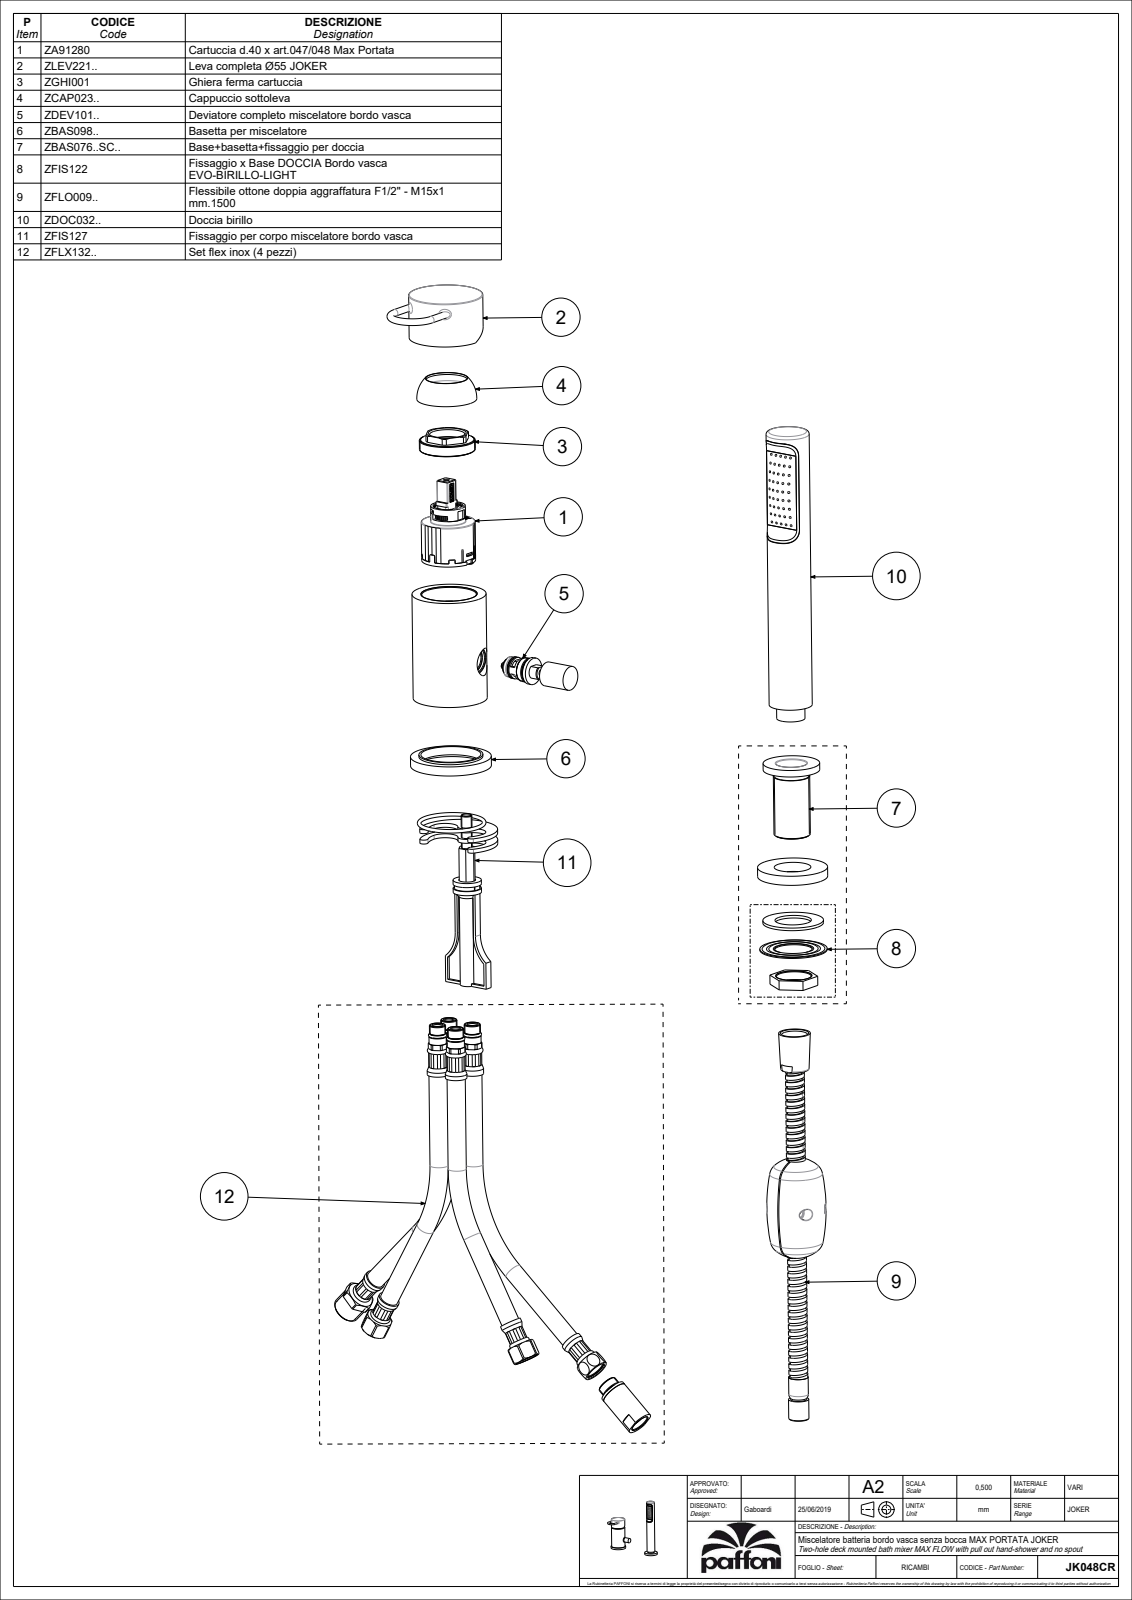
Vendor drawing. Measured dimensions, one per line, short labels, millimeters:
name: JK048CR
written by: CREO PARAMETRIC BY PTC INC, 2020044 (CONFIG_CONTROL_DESIGN)
unit: mm
bodies: 5 solids, 1689 faces (828 planar, 516 cylindrical, 345 other)
size: 222 × 206 × 88.87
volume: 267 154 mm³; area: 129 157 mm²
holes: 45× ⌀1.5, 5× ⌀8, 4× ⌀11, 4× ⌀13, 2× ⌀3.3, 2× ⌀5, 2× ⌀7, 2× ⌀7.5, 2× ⌀9.8, 1× ⌀3, 1× ⌀4, 1× ⌀5.5
bosses: 4× ⌀5, 2× ⌀55, 2× ⌀12.8, 2× ⌀10.5, 2× ⌀10, 1× ⌀60, 1× ⌀52, 1× ⌀47.5
rounds: 21× R0.5, 12× R0.15, 12× R0.2, 11× R1.5, 10× R1.1, 9× R0.25, 8× R2, 8× R3
face distances: 2, 7, 119.3, 5, 1.5, 9, 54.3, 112.3, 213, 10
hole spacings: 7.91, 13.76, 20.01, 6.5, 13, 26.39, 4.5, 19.5
